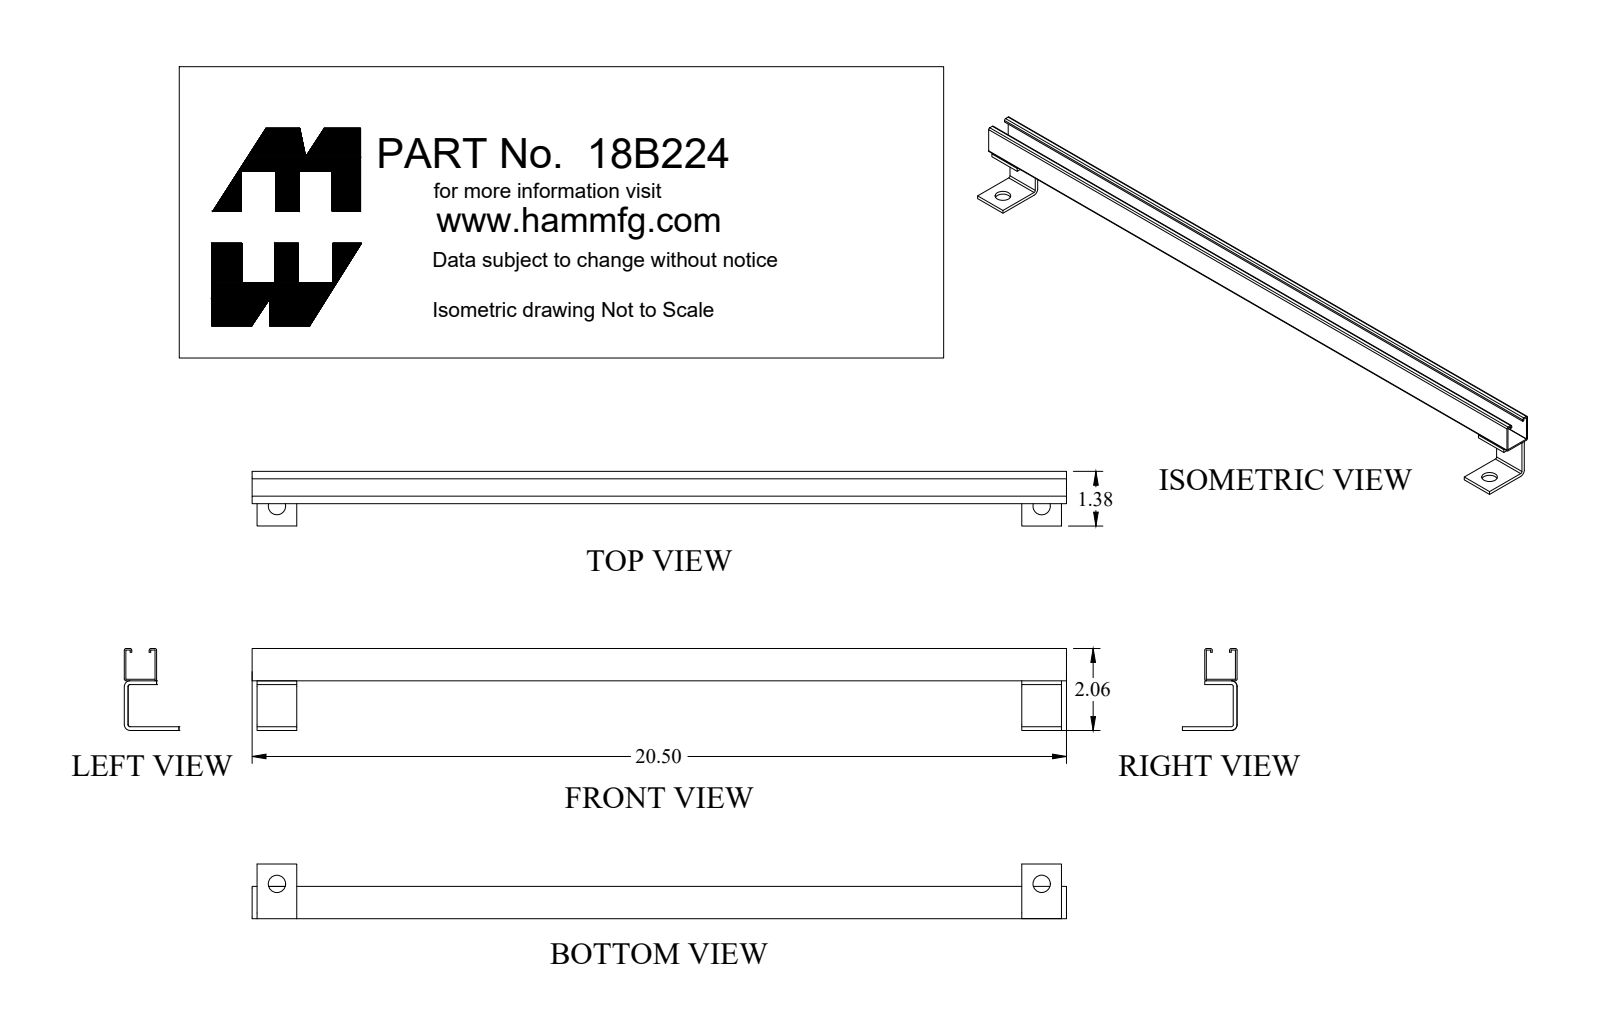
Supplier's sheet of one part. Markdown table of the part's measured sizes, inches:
| quantity | value |
| --- | --- |
| part name | 18B224 |
| STEP written by | SolidWorks 2018 (AUTOMOTIVE_DESIGN) |
| units | inches |
| bodies | 3 solids, 60 faces (38 planar, 22 cylindrical, 0 other) |
| overall size | 20.5 × 2.063 × 1.376 |
| volume | 2.79 in³ |
| surface area | 126.6 in² |
| round holes (diameter × count) | 0.437 × 2 |
| partial cylindrical surfaces (radius × count) | 0.043 × 6, 0.048 × 4, 0.143 × 4 |
| main face-to-face distances | 0.04, 0.773, 0.813, 0.733, 0.773, 0.095, 0.813, 0.733, 0.148, 0.625 |
| hole center spacings | 11.25 |
